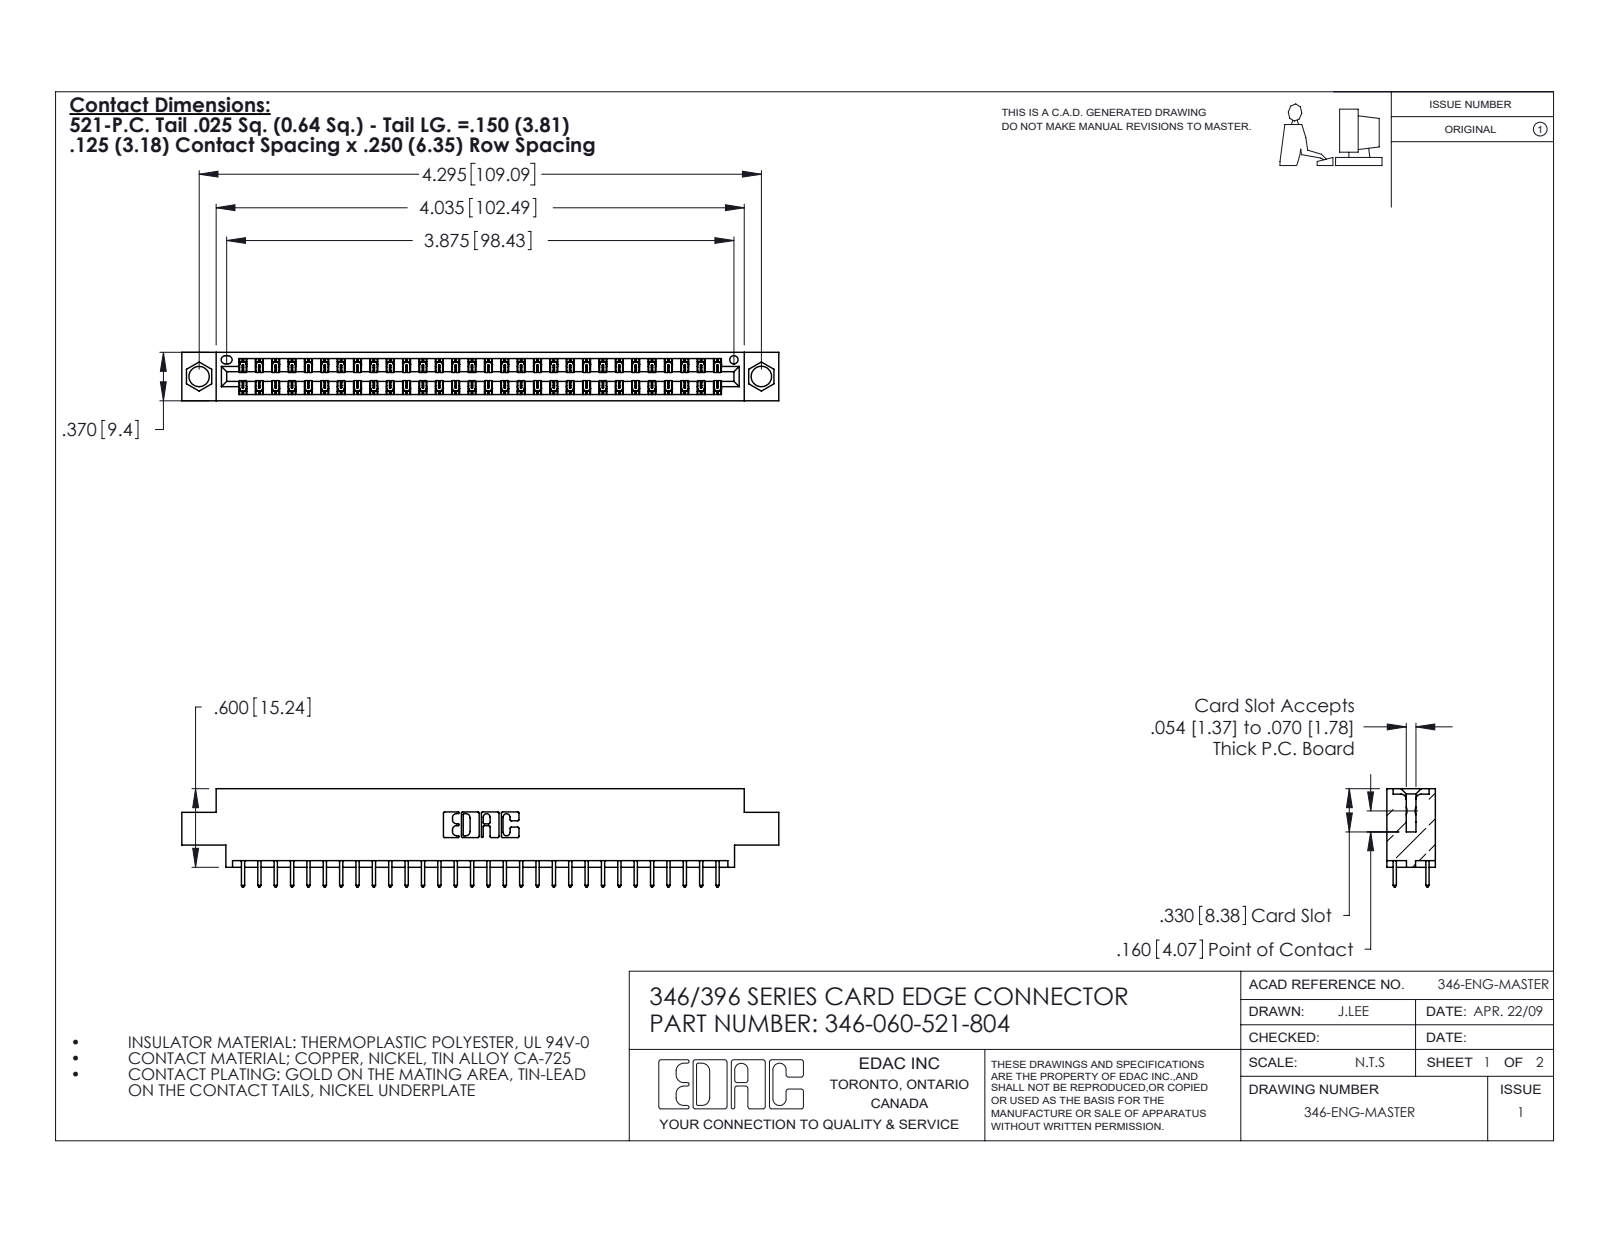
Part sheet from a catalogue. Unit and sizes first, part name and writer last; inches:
Units: inches
Overall size (bounding box): 4.56 × 0.75 × 0.37
Round holes (diameter × count): ⌀0.156 ×2, ⌀0.064 ×1
Partial cylindrical surfaces — rounded edges, fillets, slot ends (radius × count): R0.006 ×90, R0.01 ×60, R0.01 ×22, R0.007 ×6, R0.031 ×6, R0.026 ×3, R0.014 ×2, R0.022 ×2
Main face-to-face distances: 0.048, 0.322, 0.37, 0.25, 0.072, 0.298, 0.025, 0.275, 0.222, 0.148
Hole centre spacings: 0.246, 4.087, 4.295
Volume: 0.666 in³ · Surface area: 22.75 in²
Bodies: 61 solids, 3260 faces (2194 planar, 1066 cylindrical, 0 other)
Part name (STEP PRODUCT): 346-060-521-804; 345-292-001_345-293-121; 346 Part_0.170 Offset - 0.156 Dia-TH
STEP written by: SolidWorks 2020 (CONFIG_CONTROL_DESIGN)
